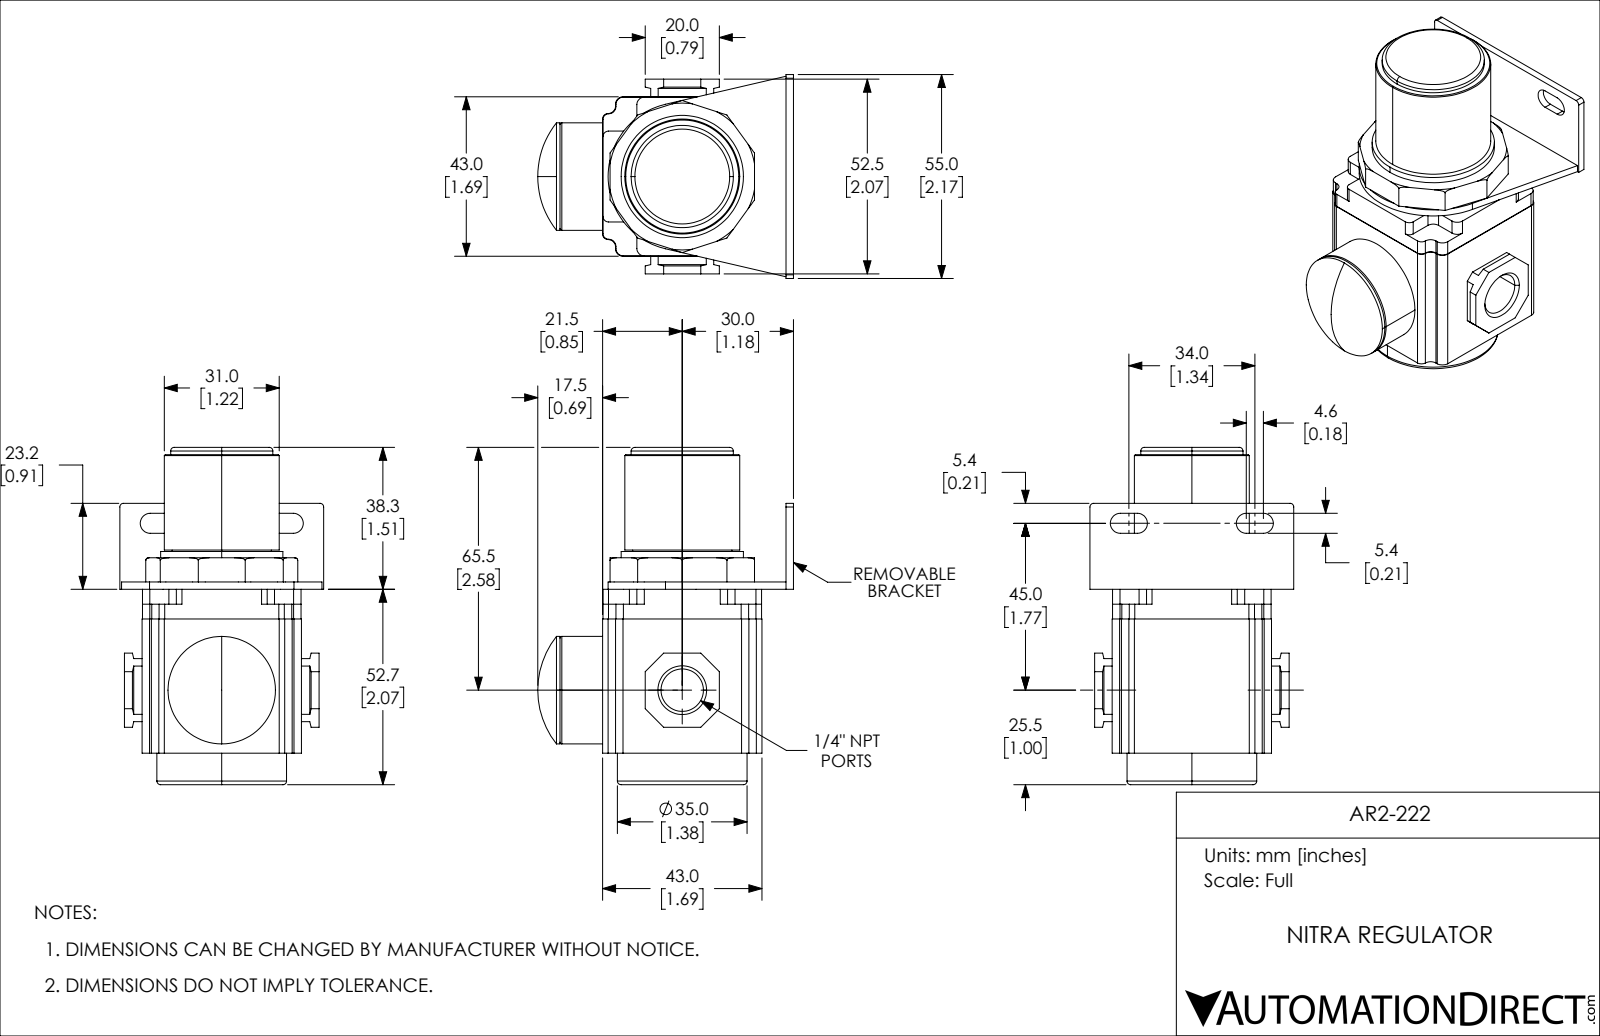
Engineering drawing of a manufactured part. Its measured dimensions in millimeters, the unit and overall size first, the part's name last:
Units: millimetres
Overall size (bounding box): 91 × 69 × 55
Round holes (diameter × count): ⌀11.45 ×1
Round bosses / shafts (diameter × count): ⌀35 ×1, ⌀33 ×1, ⌀31 ×1, ⌀29 ×1, ⌀27.58 ×1, ⌀26.78 ×1
Partial cylindrical surfaces — rounded edges, fillets, slot ends (radius × count): R2 ×24, R1.5 ×12, R2.7 ×4, R1 ×2, R20 ×1
Main face-to-face distances: 8.5, 2, 6.5, 43, 52.7, 44.2, 42.9, 54.7, 46.2, 36.3
Volume: 132 557 mm³ · Surface area: 22 852 mm²
Bodies: 1 solid, 193 faces (108 planar, 61 cylindrical, 24 other)
Part name (STEP PRODUCT): AR2-222
STEP written by: SolidWorks 2019 (CONFIG_CONTROL_DESIGN)
